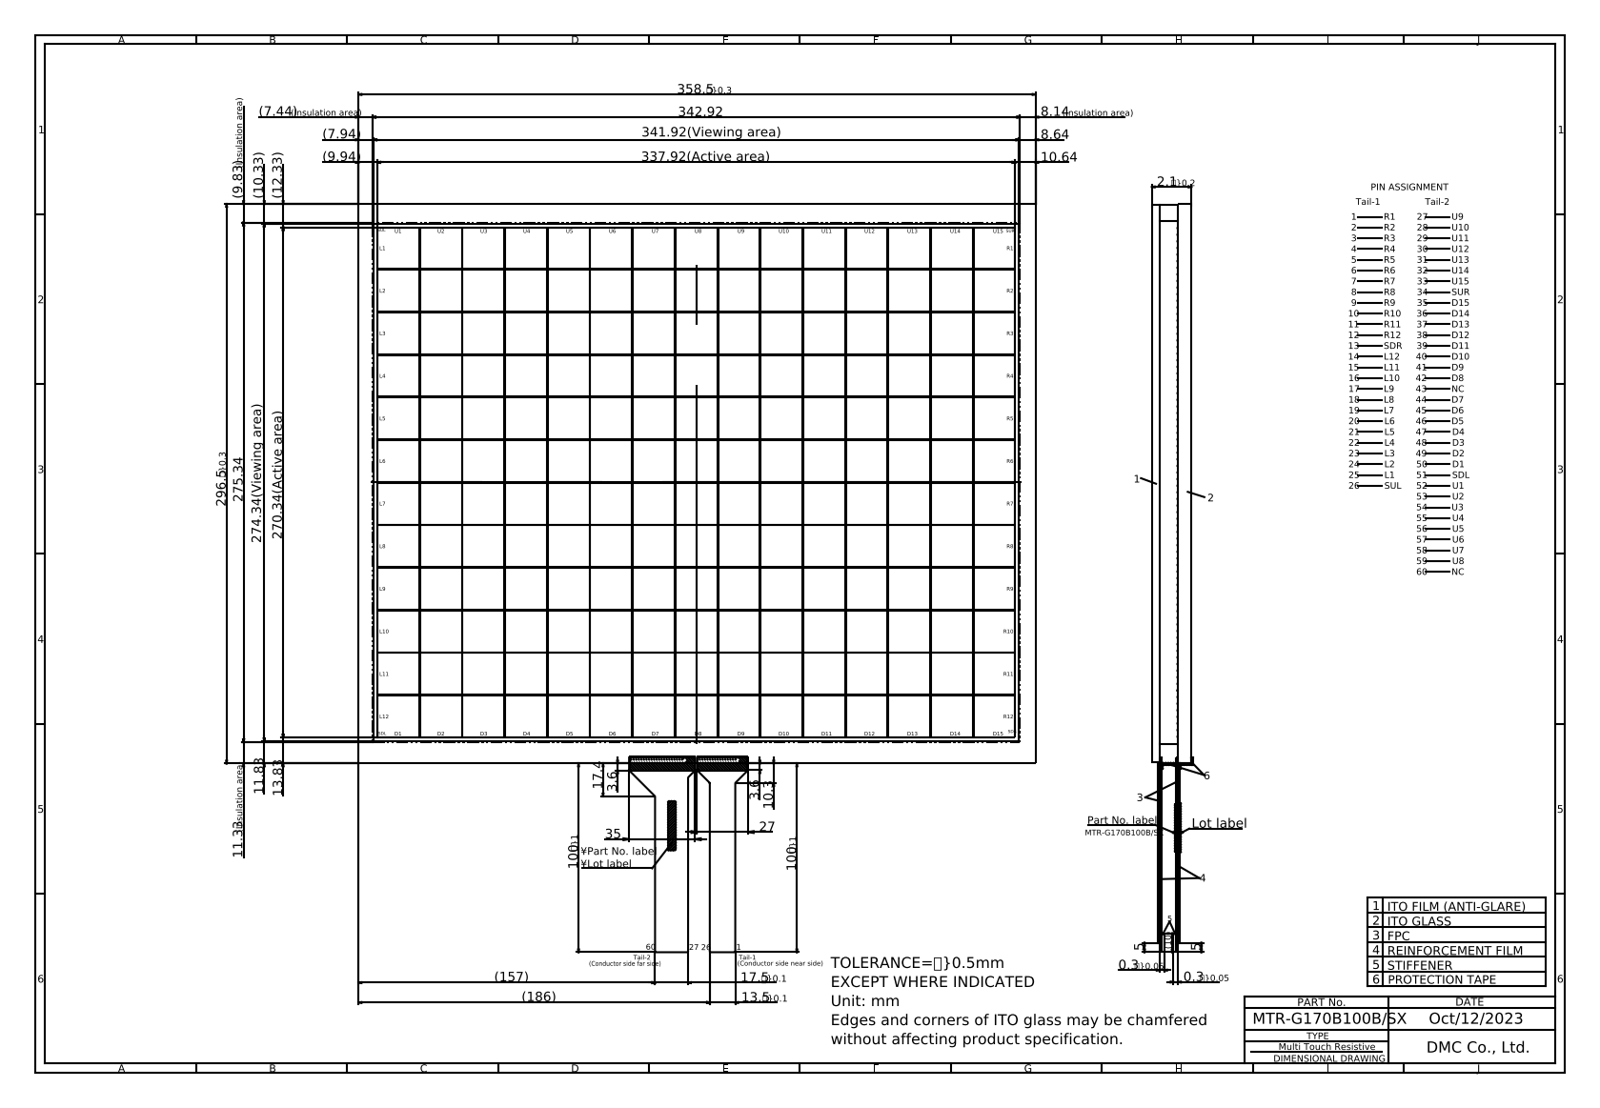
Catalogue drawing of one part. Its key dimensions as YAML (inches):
part_name: "MTR-G170B100B"
step_written_by: "Autodesk Inventor 2020 (CONFIG_CONTROL_DESIGN)"
units: inches
bodies: {solids: 1, faces: 294, planar: 282, cylindrical: 12, other: 0}
overall_size: [19.76, 17.945, 0.087]
volume: 13.63
surface_area: 344.7
partial_cylinders:
  - {radius: 0.039, count: 8}
  - {radius: 0.008, count: 4}
face_to_face_distances: [0.083, 0.071, 0.075, 0.079, 11.673, 14.114, 0.016, 0.087, 0.02, 0.028]
